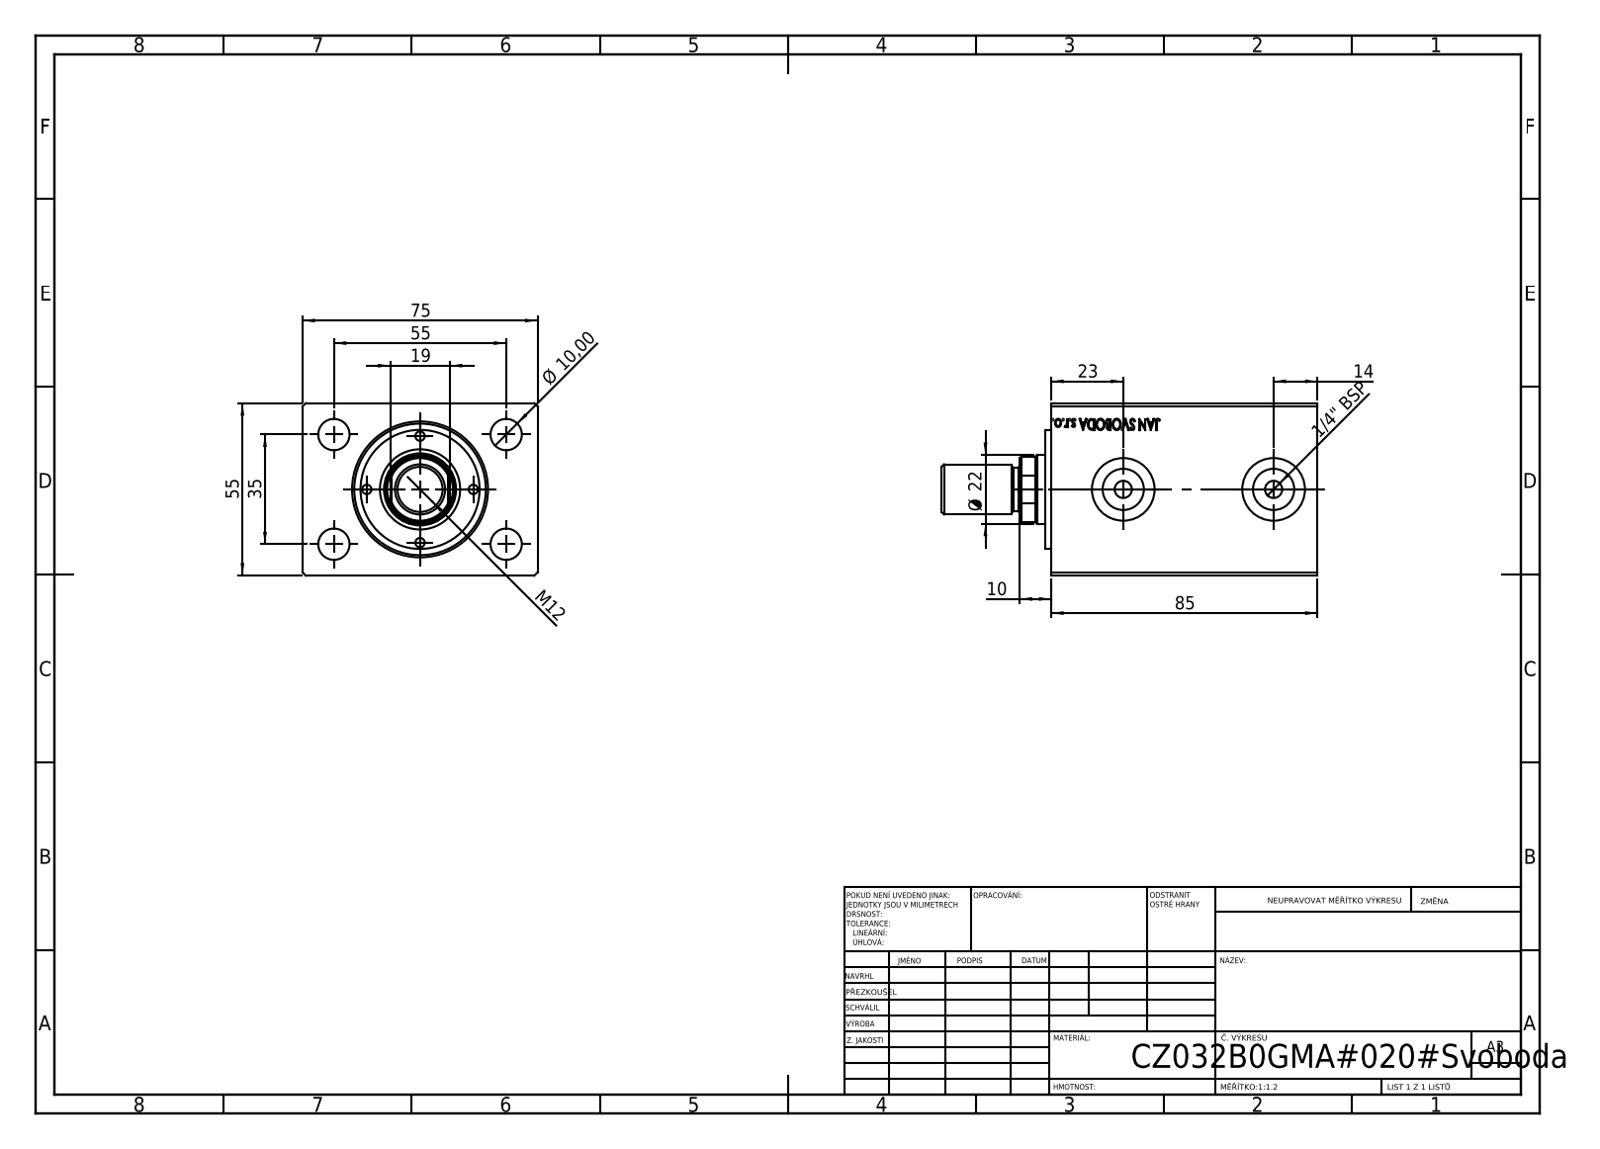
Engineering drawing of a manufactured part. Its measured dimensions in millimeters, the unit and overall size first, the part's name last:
Units: millimetres
Overall size (bounding box): 120 × 75 × 55
Round holes (diameter × count): ⌀3 ×4, ⌀10 ×4, ⌀5.5 ×2, ⌀13.16 ×2, ⌀20 ×2, ⌀10.5 ×1, ⌀22 ×1, ⌀23 ×1, ⌀32 ×1, ⌀36 ×1, ⌀42 ×1
Round bosses / shafts (diameter × count): ⌀38 ×1, ⌀16 ×1, ⌀14 ×1
Partial cylindrical surfaces — rounded edges, fillets, slot ends (radius × count): R10.5 ×1
Main face-to-face distances: 55, 75, 85, 71.2, 13.8, 10, 8.2, 1.8, 84.8, 13.6
Hole centre spacings: 17, 20.41, 24.04, 27.5, 32.6, 44.12, 47.82, 34
Volume: 328 027 mm³ · Surface area: 60 030 mm²
Bodies: 4 solids, 887 faces (403 planar, 62 cylindrical, 422 other)
Part name (STEP PRODUCT): V500CZ_B_VC; V500CZ_MALE_METRIC; V500CZ
STEP written by: SolidWorks 2019 (CONFIG_CONTROL_DESIGN)
